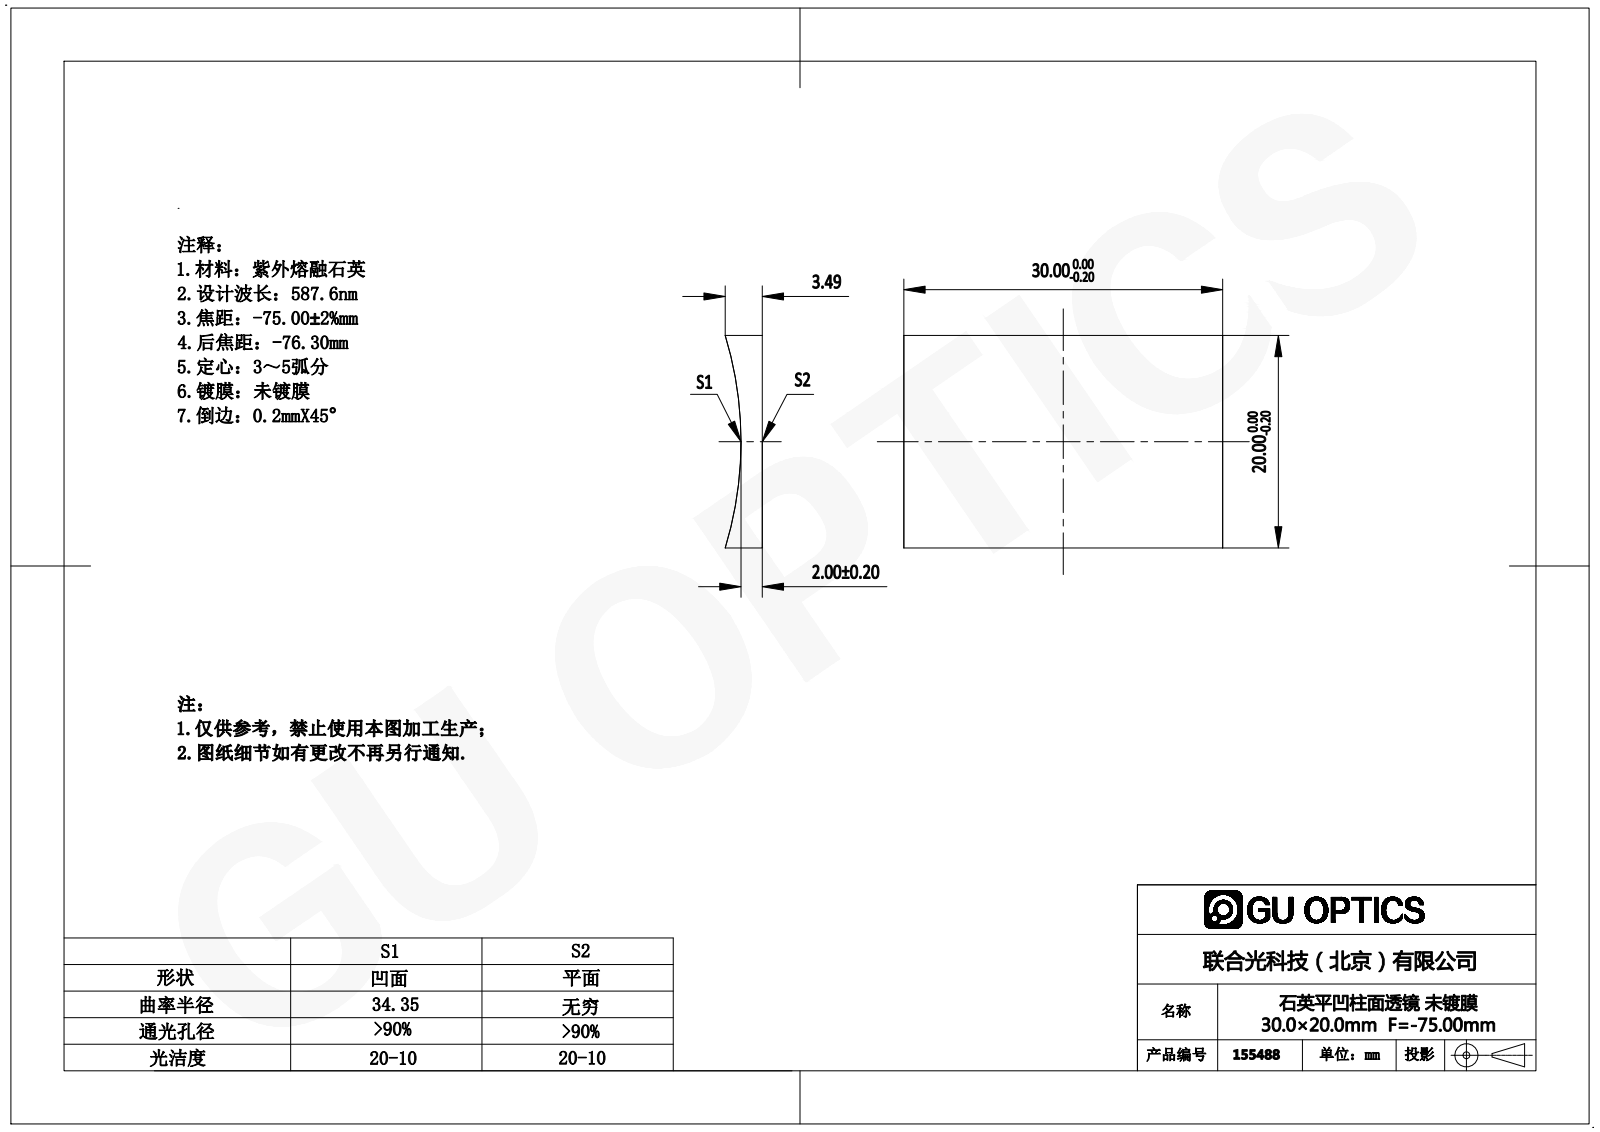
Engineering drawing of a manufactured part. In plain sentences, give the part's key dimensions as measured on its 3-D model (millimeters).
The part is named "155488". Its 3-D file was written by "SolidWorks 2016 (AUTOMOTIVE_DESIGN)". It is 1 solid with 6 faces: 5 planar, 1 cylindrical and 0 other. Overall it measures 30 by 20 by 3.49 millimeters. Its volume is 1 495 cubic millimeters and its surface area 1 518 square millimeters. Partial cylindrical surfaces (rounded edges, fillets, slot ends): 1 of radius 34.35. The main face-to-face distances are 20, 30.
